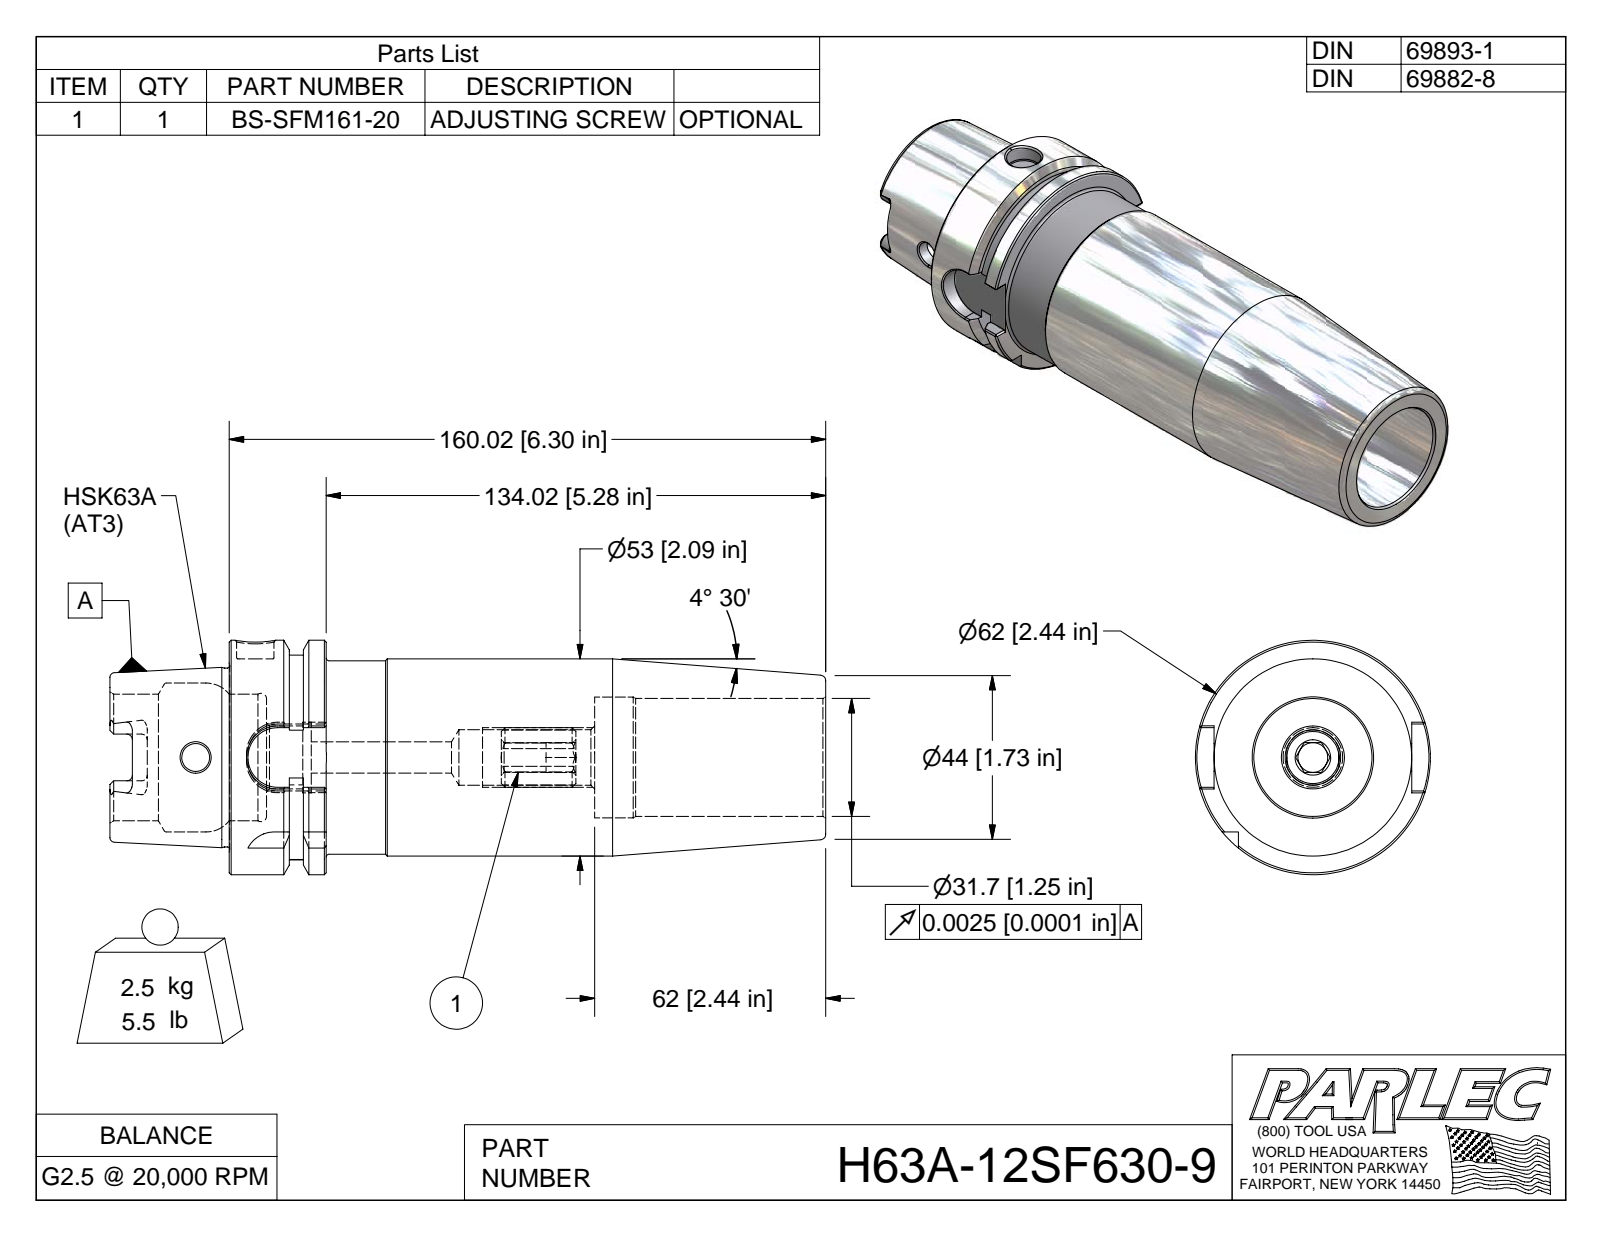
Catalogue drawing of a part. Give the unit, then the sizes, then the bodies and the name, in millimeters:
Units: millimetres
Overall size (bounding box): 192 × 63 × 63
Round holes (diameter × count): ⌀7.5 ×1, ⌀10 ×1, ⌀16.9 ×1, ⌀19 ×1, ⌀31.7 ×1, ⌀32.5 ×1, ⌀34 ×1, ⌀40 ×1
Round bosses / shafts (diameter × count): ⌀63 ×1, ⌀53 ×1, ⌀52 ×1, ⌀48 ×1
Partial cylindrical surfaces — rounded edges, fillets, slot ends (radius × count): R1.5 ×6, R8 ×5, R2.9 ×4, R27.5 ×1
Main face-to-face distances: 26, 6.1, 9.9, 98, 72, 10, 16, 88, 160, 150
Volume: 300 000 mm³ · Surface area: 53 830 mm²
Bodies: 2 solids, 167 faces (65 planar, 37 cylindrical, 65 other)
Part name (STEP PRODUCT): H63A-12SF630-9; H63A-12SF630-9-1; BS-SFM161-20
STEP written by: Autodesk Inventor 2009 (AUTOMOTIVE_DESIGN)
